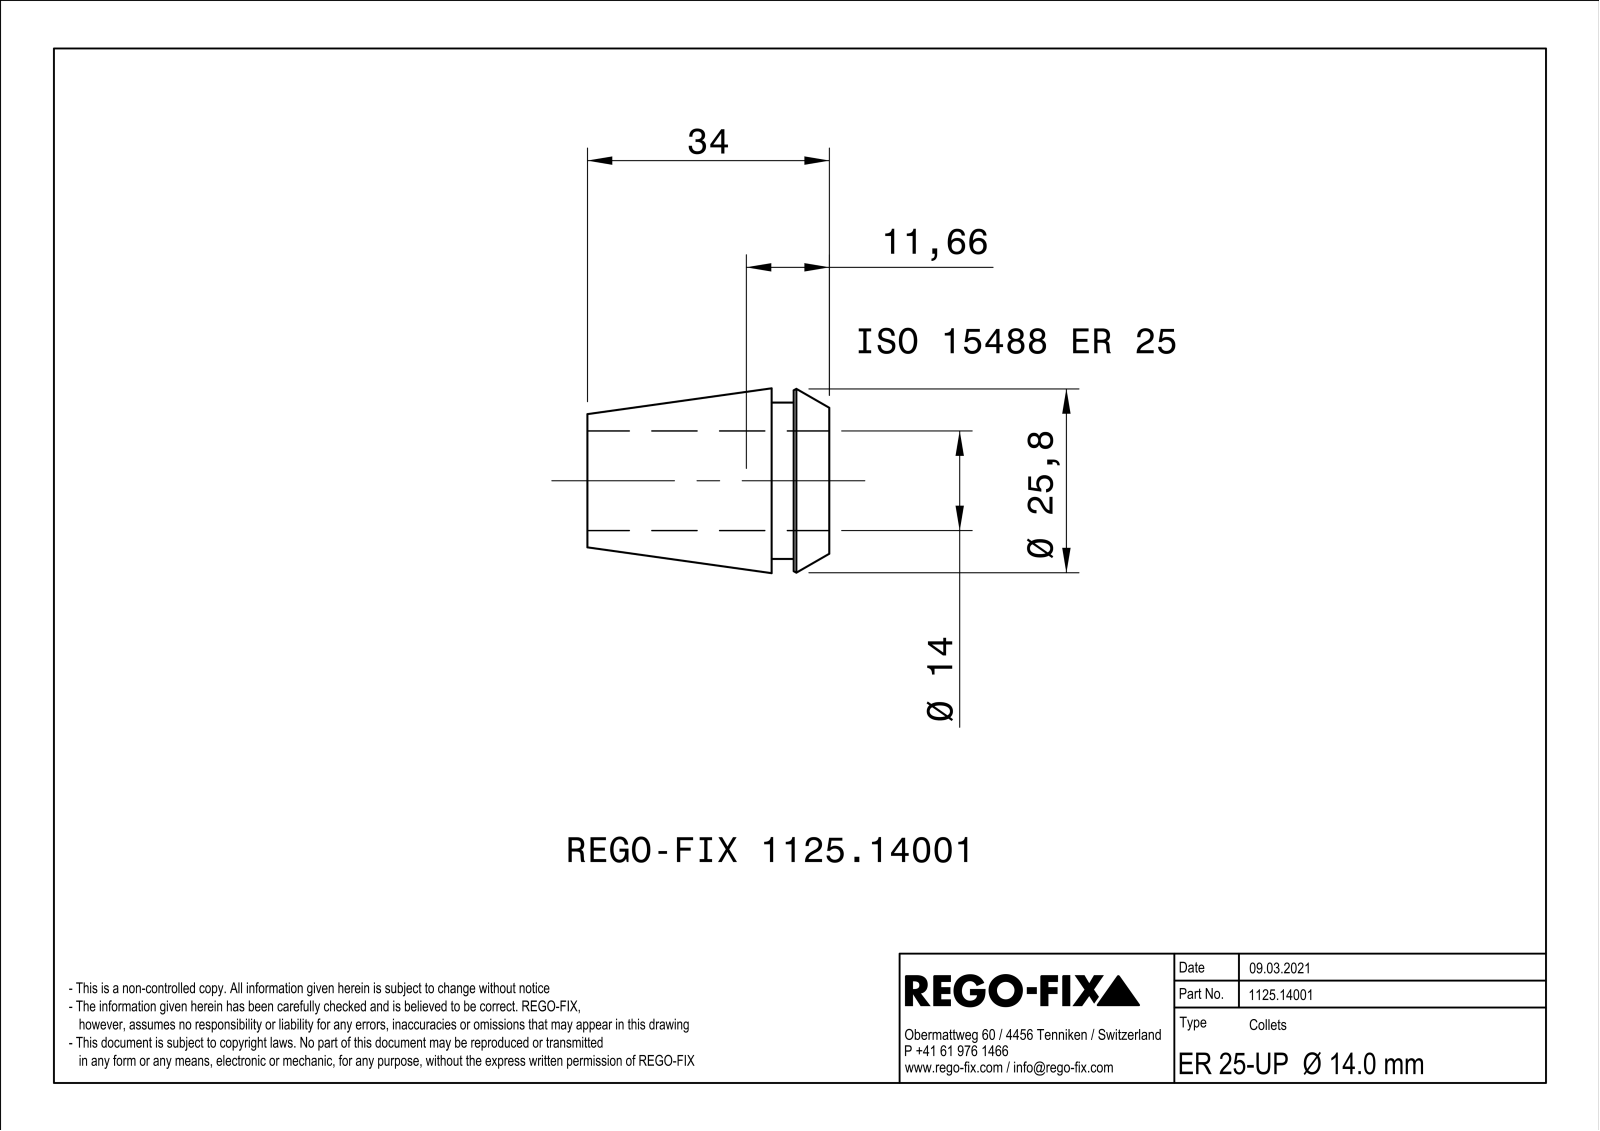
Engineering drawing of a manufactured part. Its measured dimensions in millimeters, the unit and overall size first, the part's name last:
Units: millimetres
Overall size (bounding box): 34 × 25.99 × 25.99
Round holes (diameter × count): ⌀14 ×1
Round bosses / shafts (diameter × count): ⌀22 ×1
Partial cylindrical surfaces — rounded edges, fillets, slot ends (radius × count): R0.4 ×8
Main face-to-face distances: 0.8, 8.1, 5, 3.1, 34, 29, 25.9
Volume: 6 732 mm³ · Surface area: 7 794 mm²
Bodies: 1 solid, 177 faces (72 planar, 25 cylindrical, 80 other)
Part name (STEP PRODUCT): NOCUT
STEP written by: SIEMENS PLM Software Solid Edge ST10 (AUTOMOTIVE_DESIGN)
